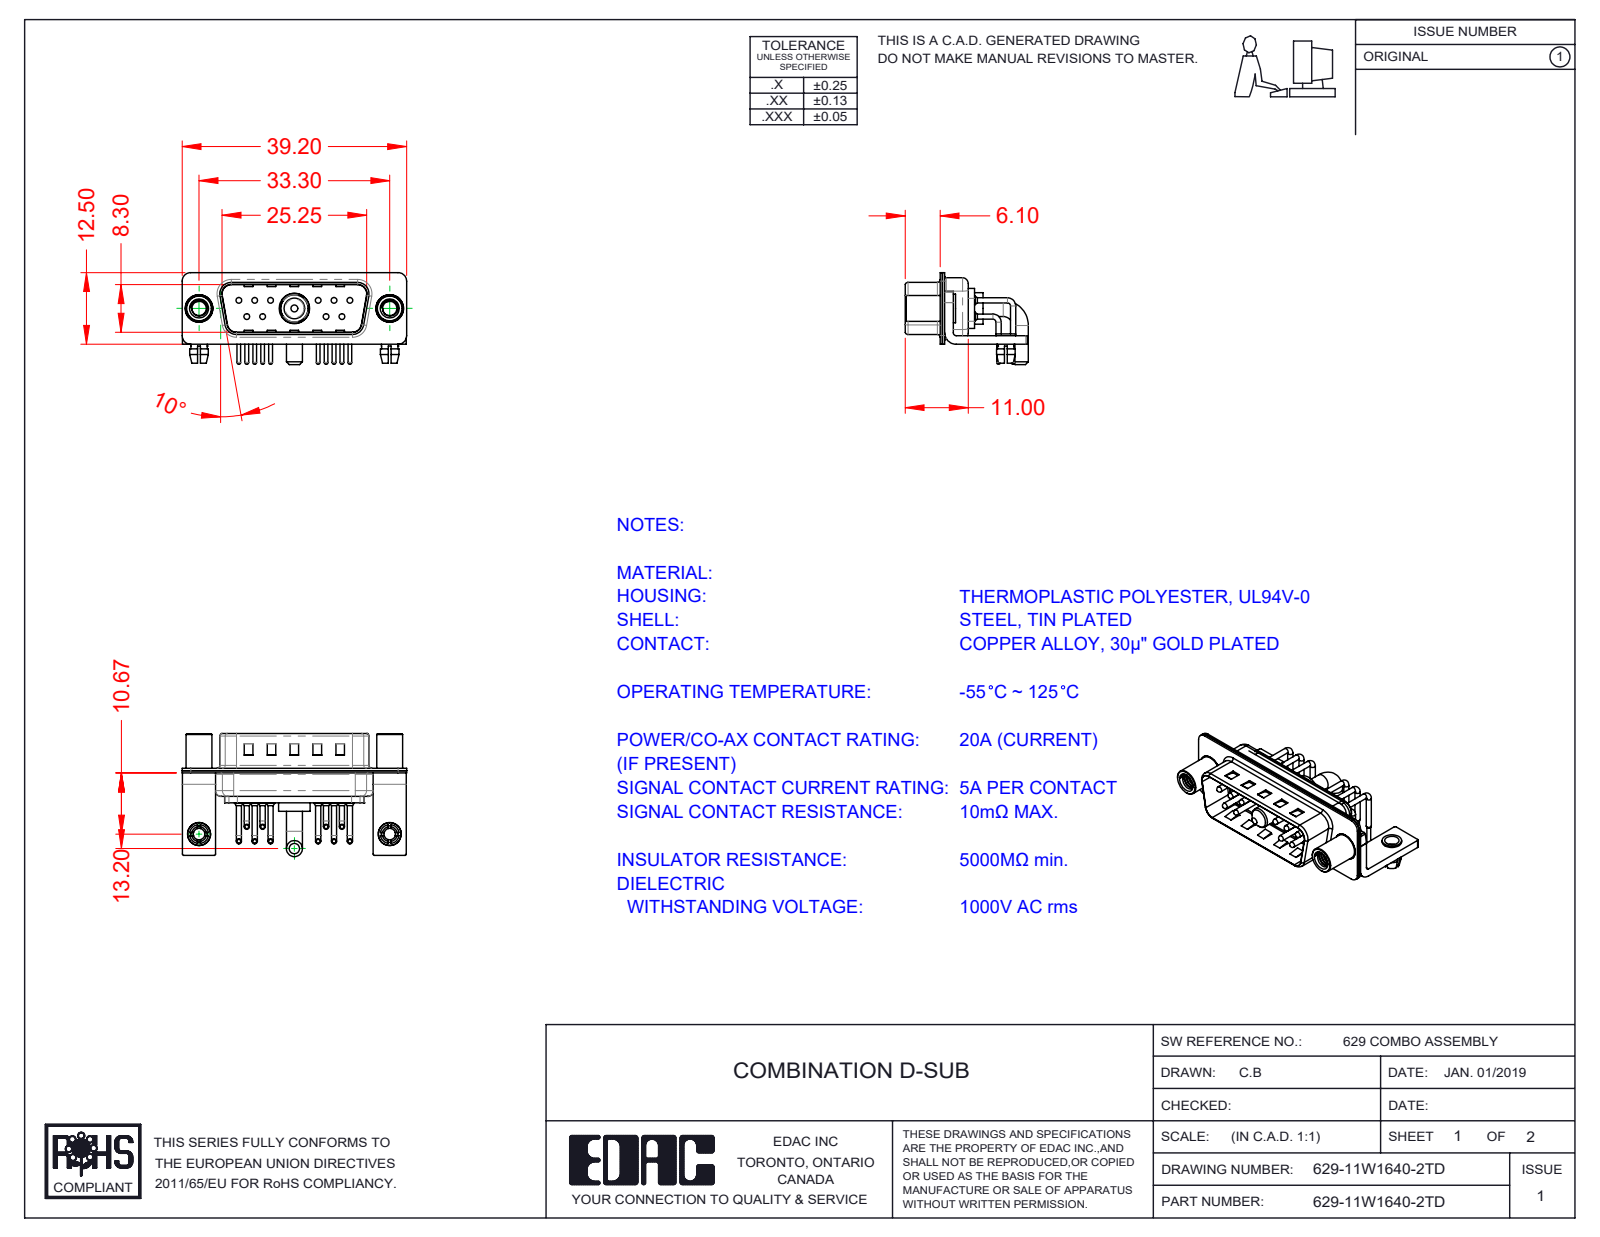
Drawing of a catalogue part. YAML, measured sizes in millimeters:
part_name: "629Combo Shell Front_15 Contacts; 629Combo Contact Row 1; Power Pin_20A RA; 629Combo Board Lock (+6 more)"
step_written_by: "SolidWorks 2020 (CONFIG_CONTROL_DESIGN)"
units: millimeters
bodies: {solids: 21, faces: 1686, planar: 868, cylindrical: 622, other: 196}
overall_size: [39.2, 21.5, 16.05]
volume: 2483
surface_area: 6368
round_holes:
  - {diameter: 2, count: 12}
  - {diameter: 0.75, count: 10}
  - {diameter: 1.6, count: 10}
  - {diameter: 2.5, count: 4}
  - {diameter: 3.2, count: 2}
  - {diameter: 4, count: 2}
  - {diameter: 4.8, count: 2}
  - {diameter: 4.85, count: 1}
  - {diameter: 5.3, count: 1}
round_bosses_or_shafts:
  - {diameter: 0.9, count: 20}
  - {diameter: 1.5, count: 10}
  - {diameter: 1, count: 10}
  - {diameter: 0.65, count: 10}
  - {diameter: 5, count: 2}
  - {diameter: 4.9, count: 2}
  - {diameter: 4.5, count: 2}
  - {diameter: 4, count: 2}
partial_cylinders:
  - {radius: 0.25, count: 16}
  - {radius: 1.5, count: 16}
  - {radius: 2, count: 13}
  - {radius: 1.01, count: 10}
  - {radius: 0.5, count: 9}
  - {radius: 1.6, count: 8}
  - {radius: 1, count: 7}
  - {radius: 0.6, count: 4}
face_to_face_distances: [0.4, 0.8, 1.5, 9.5, 9.1, 8.7, 9.9, 0.6, 1.9, 0.75]
hole_center_spacings: [3.16, 2.77, 13.85, 11.08, 16.62, 5.03, 5.04, 5.54]
